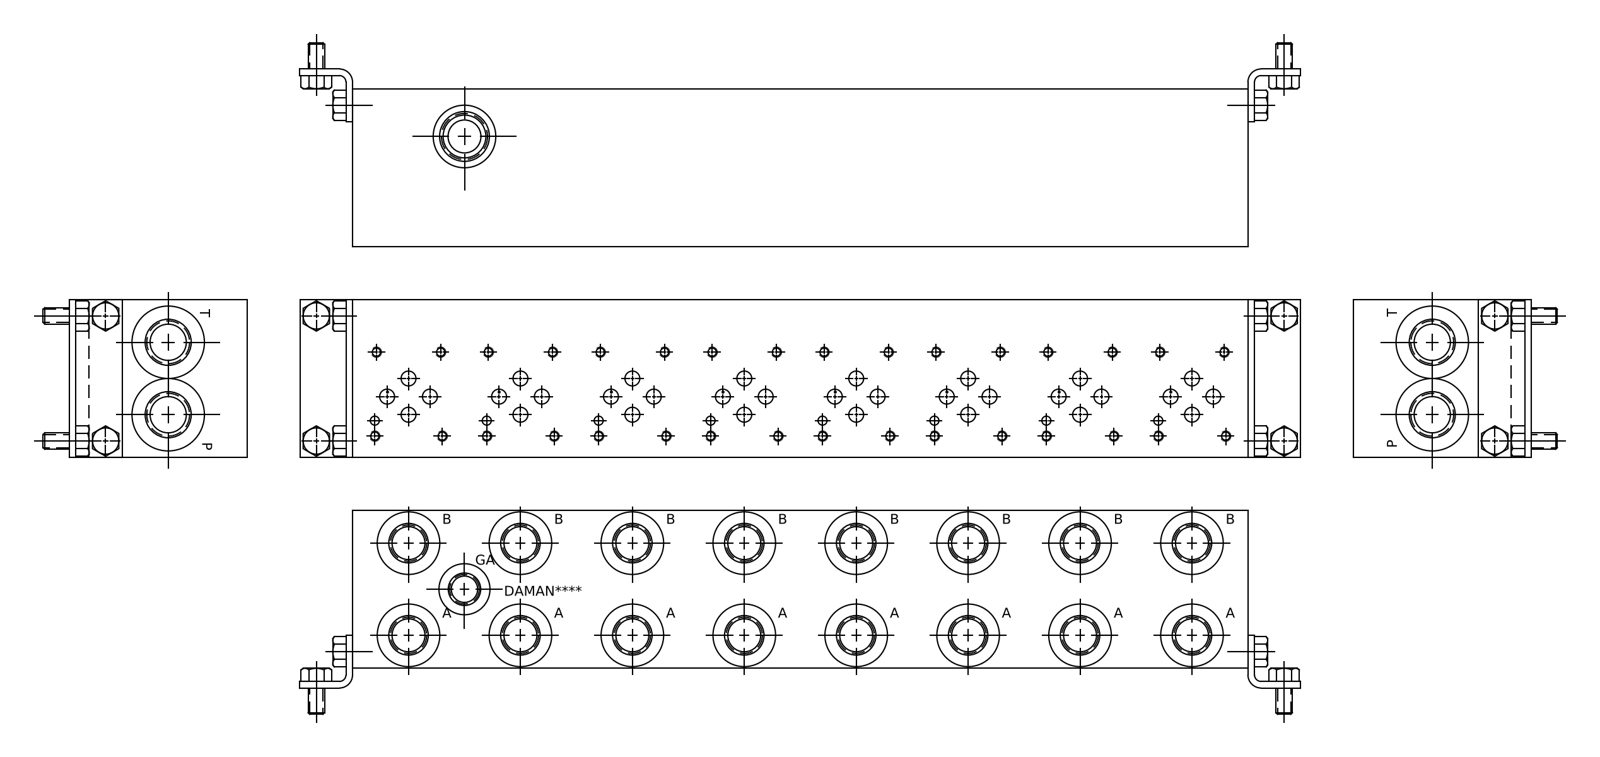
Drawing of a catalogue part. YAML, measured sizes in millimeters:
part_name: "Part_AD03P082S_C_3D"
step_written_by: "Autodesk Inventor 2020 (AUTOMOTIVE_DESIGN)"
units: millimeters
bodies: {solids: 1, faces: 1224, planar: 565, cylindrical: 223, other: 436}
overall_size: [431.8, 76.2, 76.2]
volume: 2323000
surface_area: 188451
round_holes:
  - {diameter: 3.78, count: 32}
  - {diameter: 4.83, count: 32}
  - {diameter: 7.14, count: 24}
  - {diameter: 15.88, count: 16}
  - {diameter: 17.5, count: 16}
  - {diameter: 19.05, count: 16}
  - {diameter: 19.25, count: 16}
  - {diameter: 30.63, count: 16}
  - {diameter: 3.96, count: 8}
  - {diameter: 6.35, count: 8}
  - {diameter: 22.23, count: 3}
  - {diameter: 6.53, count: 2}
face_to_face_distances: [76.2, 0.79, 75.41, 431.8, 431.01, 430.22, 15.06, 14.27, 61.14, 0.75]
hole_center_spacings: [107.95, 53.98, 215.9, 161.93, 53.97, 116.74, 161.92, 44.45]
